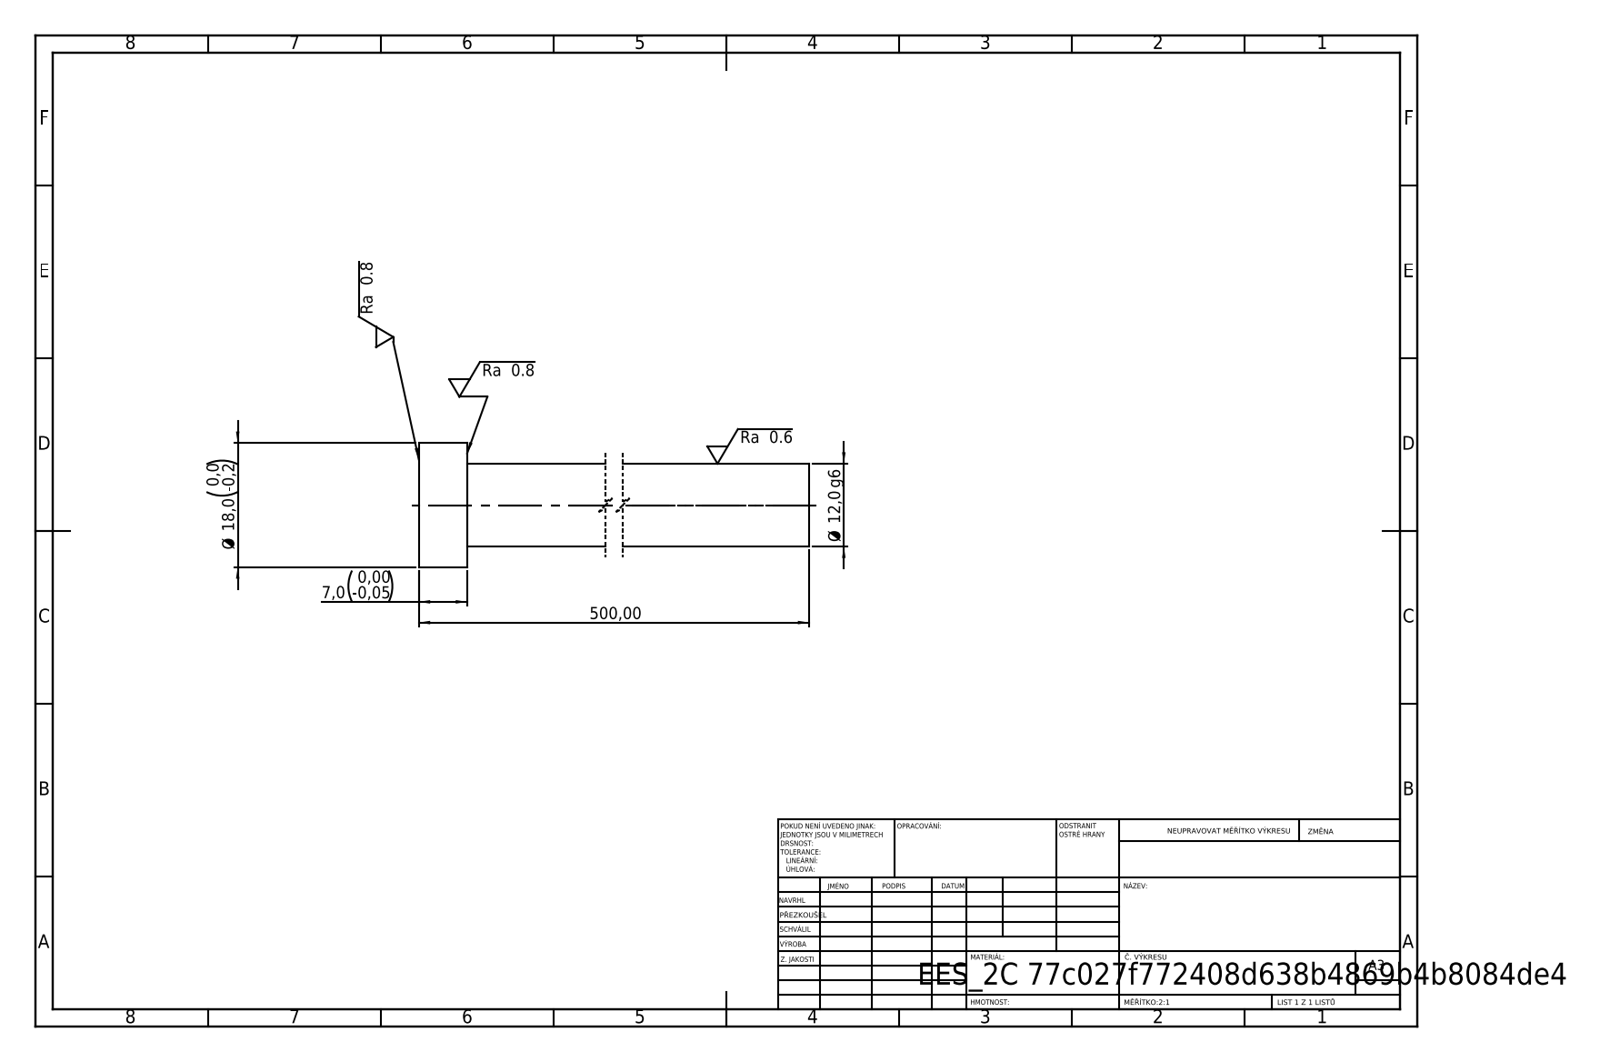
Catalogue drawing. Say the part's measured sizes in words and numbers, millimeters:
Its 3-D file was written by "SolidWorks 2019 (CONFIG_CONTROL_DESIGN)". It is 1 solid with 7 faces: 3 planar, 4 cylindrical and 0 other. Overall it measures 500 by 18 by 18 millimeters. Its volume is 57 538 cubic millimeters and its surface area 19 490 square millimeters. Round bosses or shafts: 1 of diameter 18, 1 of diameter 12. The main face-to-face distances are 7, 500, 493.
